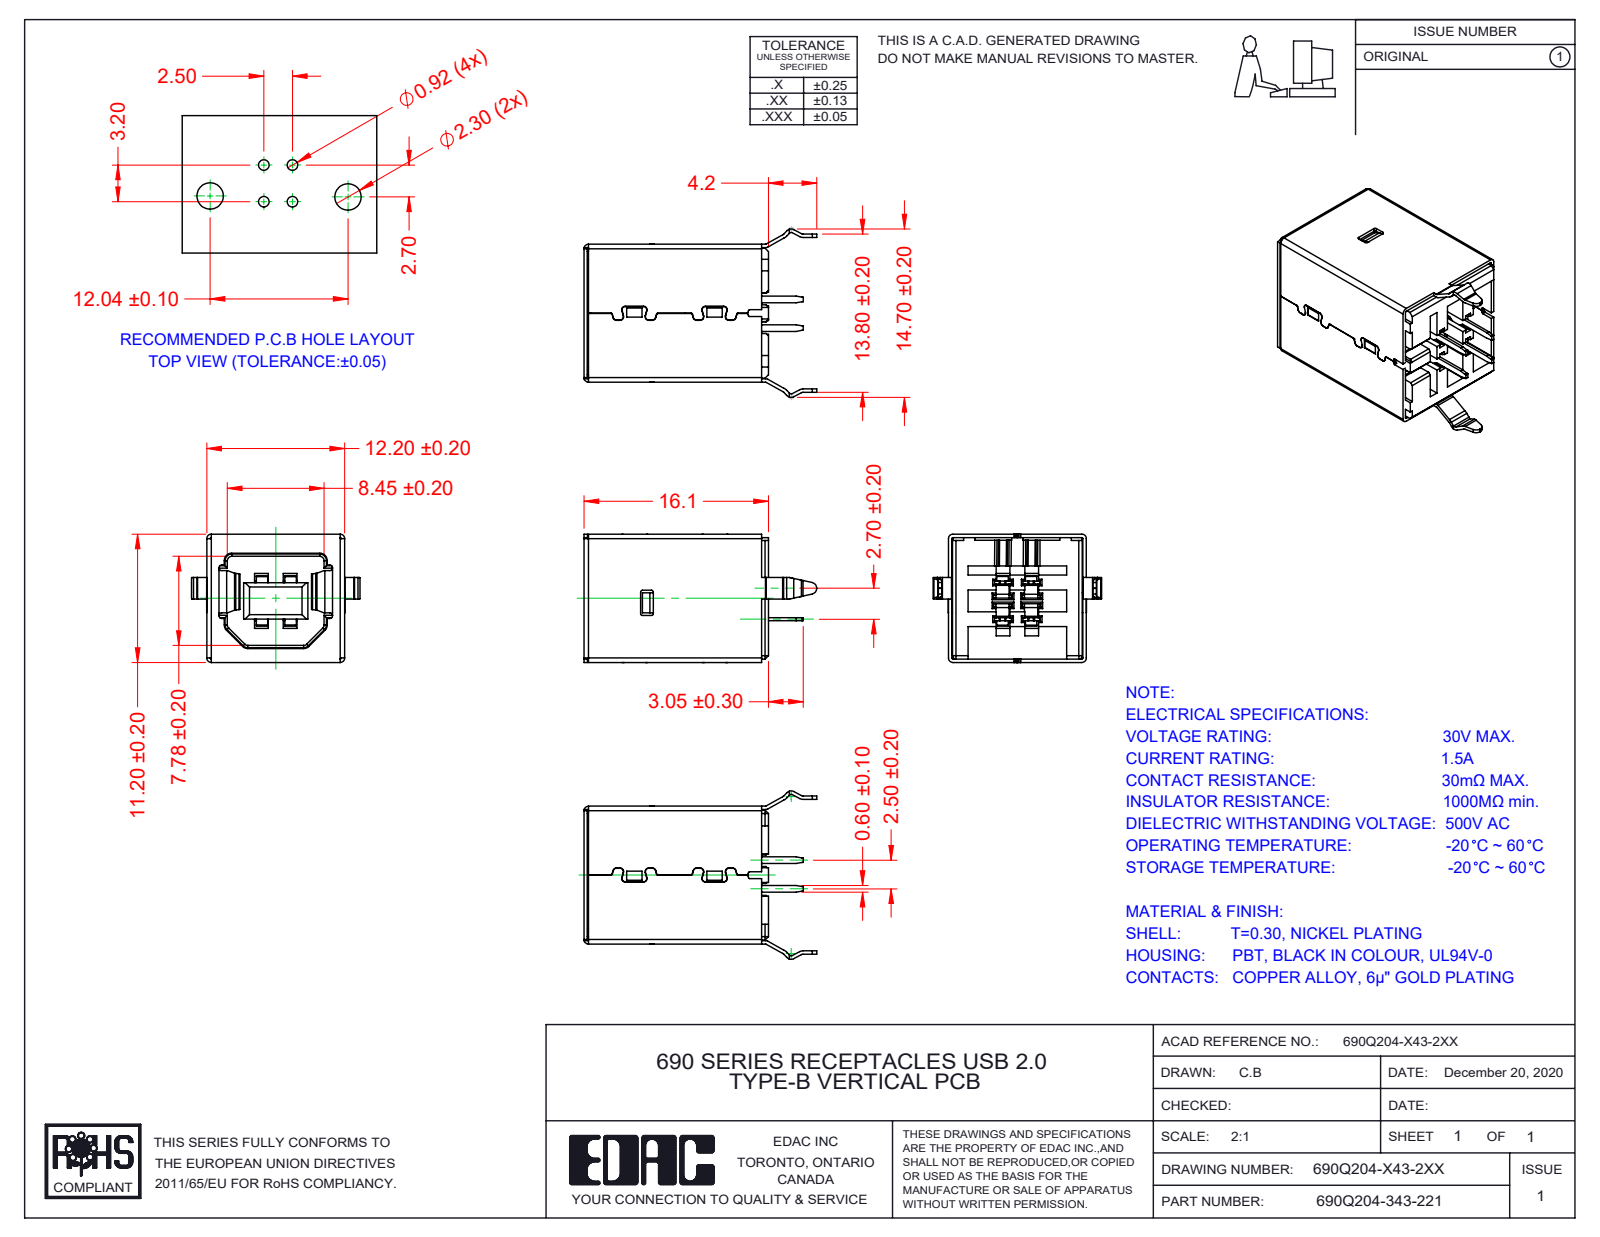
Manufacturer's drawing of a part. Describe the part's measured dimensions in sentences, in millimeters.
The part is named "690Q204-143-221; Insulator 690Q204-X43-2XX_Black; Contact 690Q204-X43-2XX; Shell 690Q204-X43-2XX". Its 3-D file was written by "SolidWorks 2020 (AUTOMOTIVE_DESIGN)". It is 6 solids with 939 faces: 698 planar, 227 cylindrical and 14 other. Overall it measures 20.32 by 14.7 by 11.2 millimeters. Its volume is 1 327 cubic millimeters and its surface area 3 612 square millimeters. Partial cylindrical surfaces (rounded edges, fillets, slot ends): 24 of radius 0.3, 17 of radius 0.1, 16 of radius 0.15, 10 of radius 0.2, 10 of radius 0.4, 8 of radius 0.32, 8 of radius 0.5, 6 of radius 0.25. The main face-to-face distances are 10.9, 11.74, 0.35, 11.69, 11.39, 10.6, 11.2, 11.44, 12.04, 0.45.
